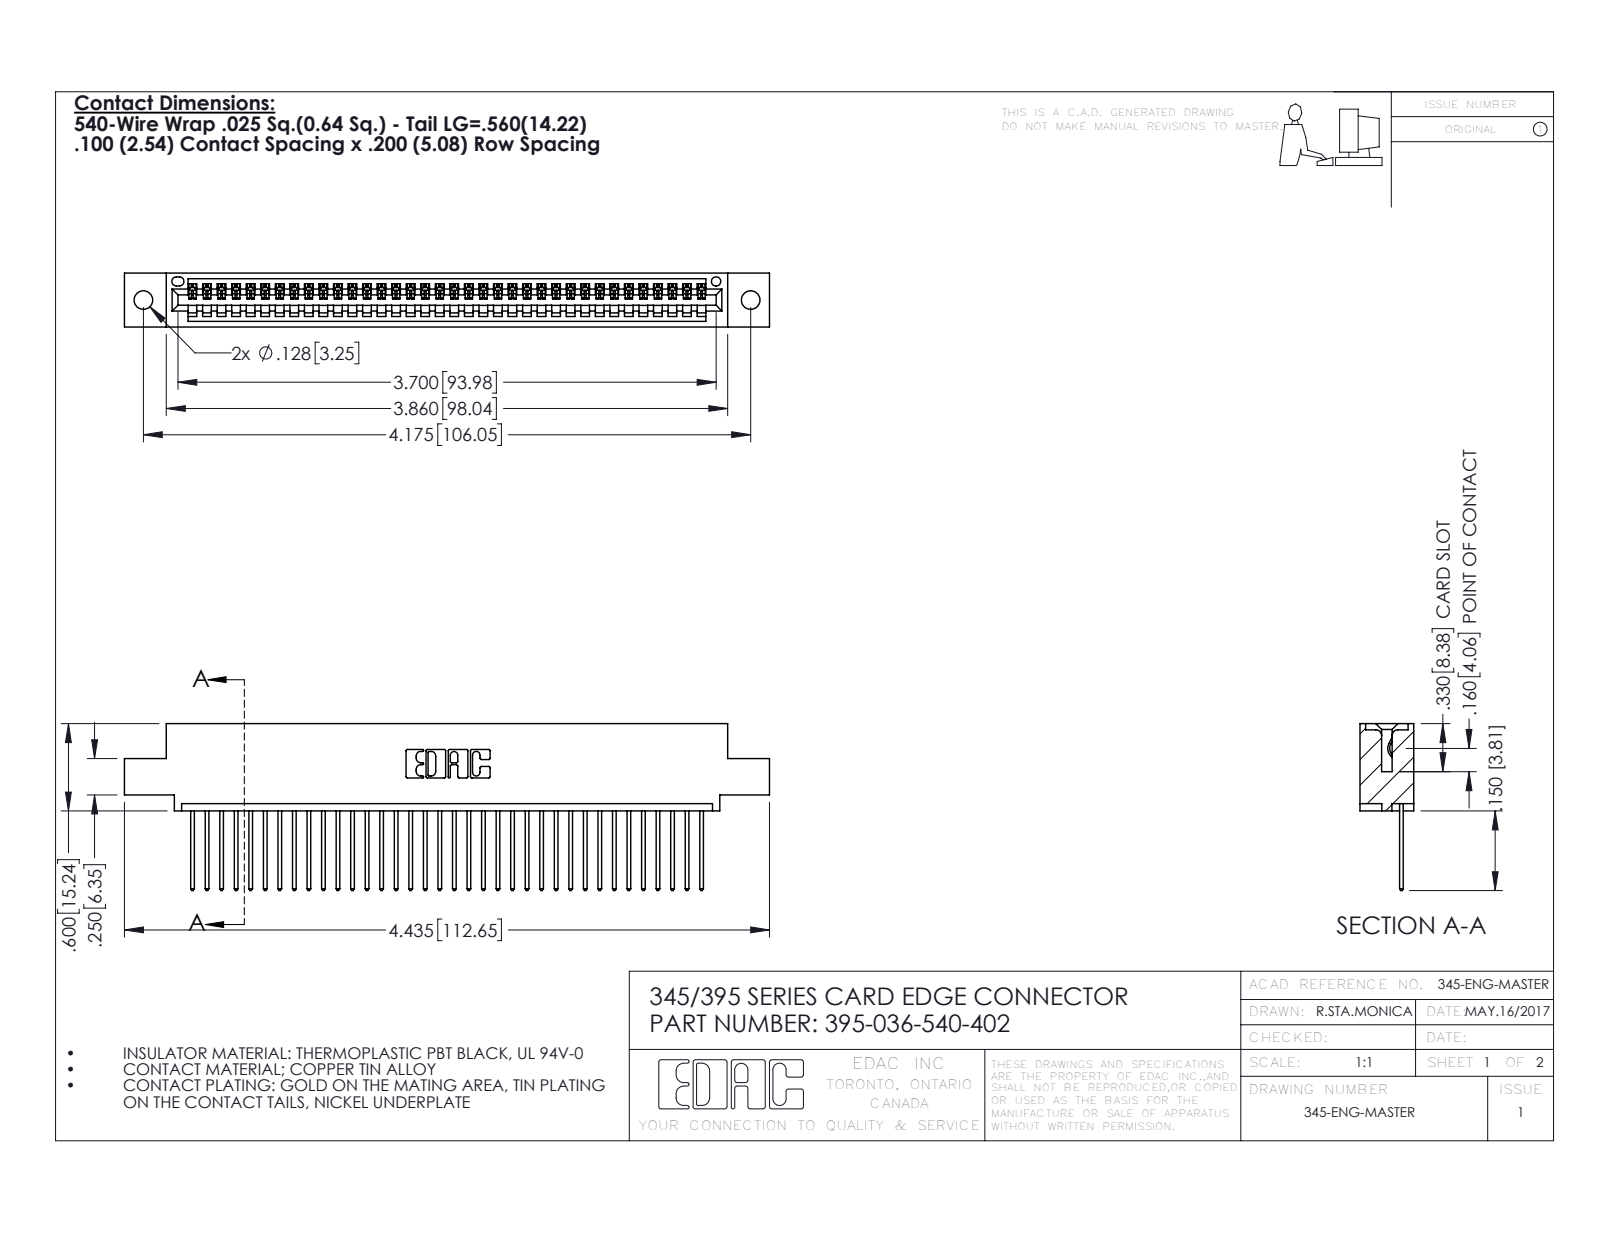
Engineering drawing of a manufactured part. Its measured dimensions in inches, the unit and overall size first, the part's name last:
Units: inches
Overall size (bounding box): 4.435 × 1.147 × 0.37
Round holes (diameter × count): ⌀0.128 ×2, ⌀0.064 ×1
Partial cylindrical surfaces — rounded edges, fillets, slot ends (radius × count): R0.006 ×72, R0.01 ×72, R0.01 ×22, R0.007 ×6, R0.031 ×6, R0.026 ×3, R0.031 ×2, R0.04 ×2
Main face-to-face distances: 0.298, 0.072, 0.37, 0.098, 0.272, 0.025, 0.2, 0.225, 0.149, 0.072
Hole centre spacings: 0.27, 3.939, 4.175
Volume: 0.646 in³ · Surface area: 21.93 in²
Bodies: 37 solids, 2218 faces (1524 planar, 694 cylindrical, 0 other)
Part name (STEP PRODUCT): 395-036-540-402; 345 Part_0.110 Offset - 0.128 Dia; 345-292-001_345-293-140
STEP written by: SolidWorks 2016 (CONFIG_CONTROL_DESIGN)
